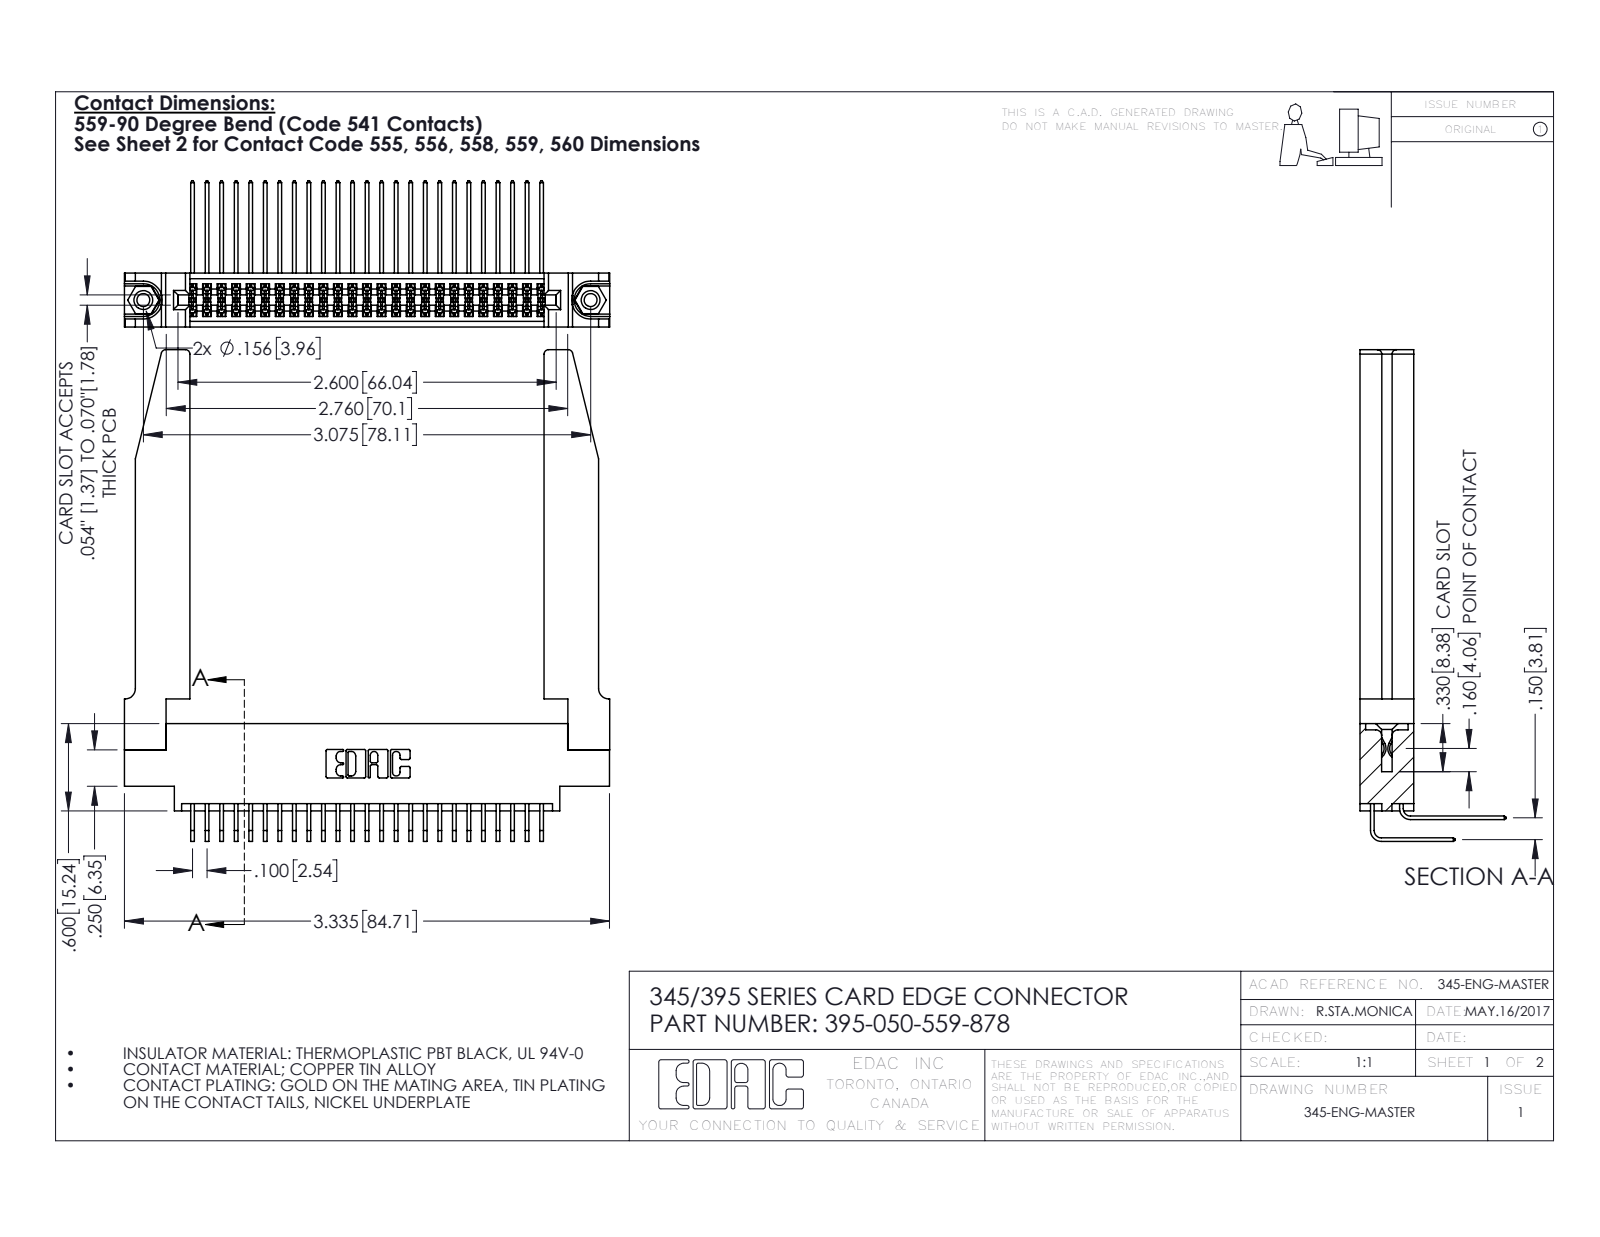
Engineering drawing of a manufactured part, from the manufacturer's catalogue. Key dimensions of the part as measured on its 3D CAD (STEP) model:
Part name (STEP PRODUCT): 395-050-559-878; 345 Part_0.170 Offset - 0.156 Dia-TH; 345-250-001_345-250-001-102; 345-292-001_559 Tail - 2 (+2 more)
STEP written by: SolidWorks 2016 (CONFIG_CONTROL_DESIGN)
Units: inches
Bodies: 55 solids, 2964 faces (1976 planar, 936 cylindrical, 52 other)
Overall size (bounding box): 3.379 × 3.336 × 1.005
Volume: 0.978 in³ · Surface area: 31.31 in²
Round holes (diameter × count): ⌀0.089 ×2, ⌀0.125 ×2, ⌀0.156 ×2, ⌀0.064 ×1
Round bosses / shafts (diameter × count): ⌀0.155 ×2
Partial cylindrical surfaces — rounded edges, fillets, slot ends (radius × count): R0.006 ×75, R0.01 ×22, R0.03 ×8, R0.007 ×6, R0.031 ×6, R0.026 ×3, R0.014 ×2, R0.019 ×2
Main face-to-face distances: 0.37, 0.072, 0.298, 0.098, 0.272, 0.025, 0.2, 0.225, 0.15, 0.175
Hole centre spacings: 0.27, 2.84, 3.075
